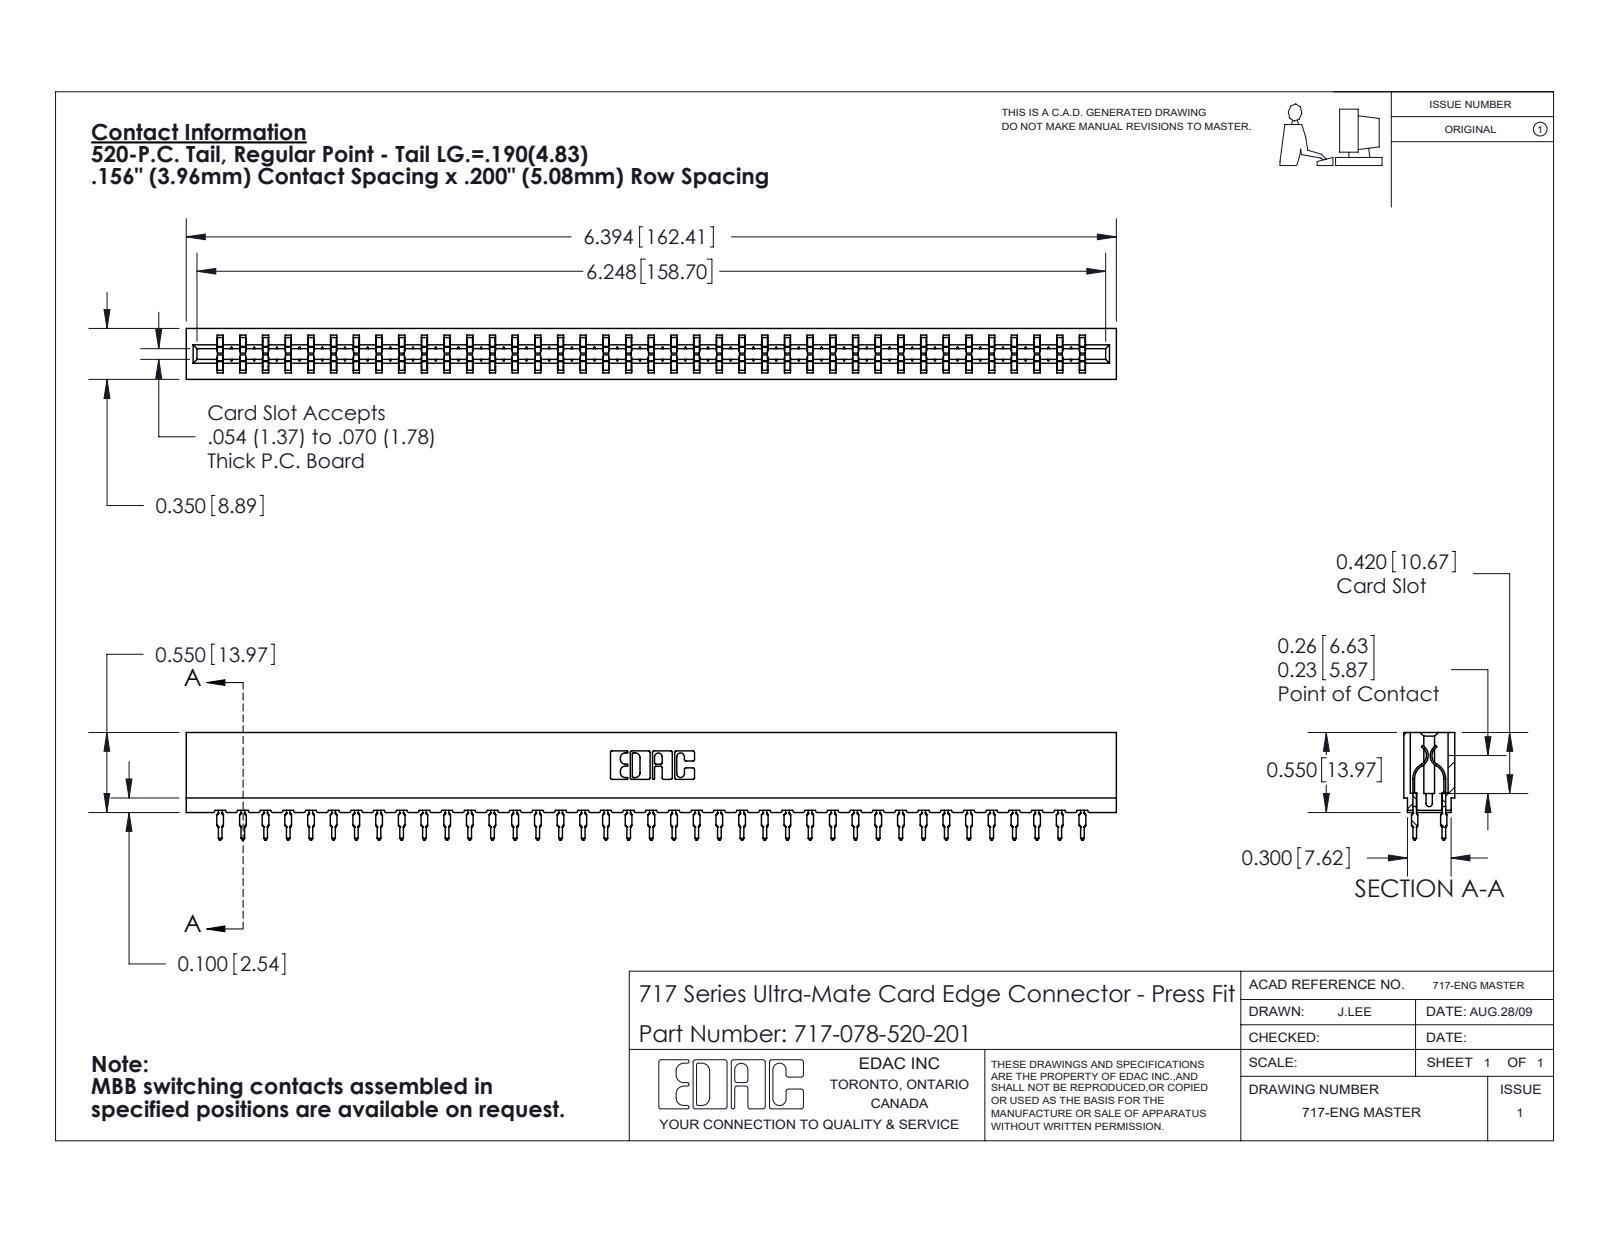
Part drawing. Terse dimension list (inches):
name: 717 Part_Insulator Option - 06; 717-078-520-201; 745-292-001_520
written by: SolidWorks 2020 (CONFIG_CONTROL_DESIGN)
unit: in
bodies: 79 solids, 7114 faces (3681 planar, 1405 cylindrical, 2028 other)
size: 6.394 × 0.739 × 0.35
volume: 0.856 in³; area: 32.57 in²
rounds: 156× R0.021, 78× R0.015, 22× R0.01, 8× R0.005, 8× R0.011, 6× R0.007, 6× R0.031, 3× R0.026
face distances: 0.212, 0.138, 0.35, 0.063, 0.287, 0.076, 0.149, 0.074, 0.045, 0.305
